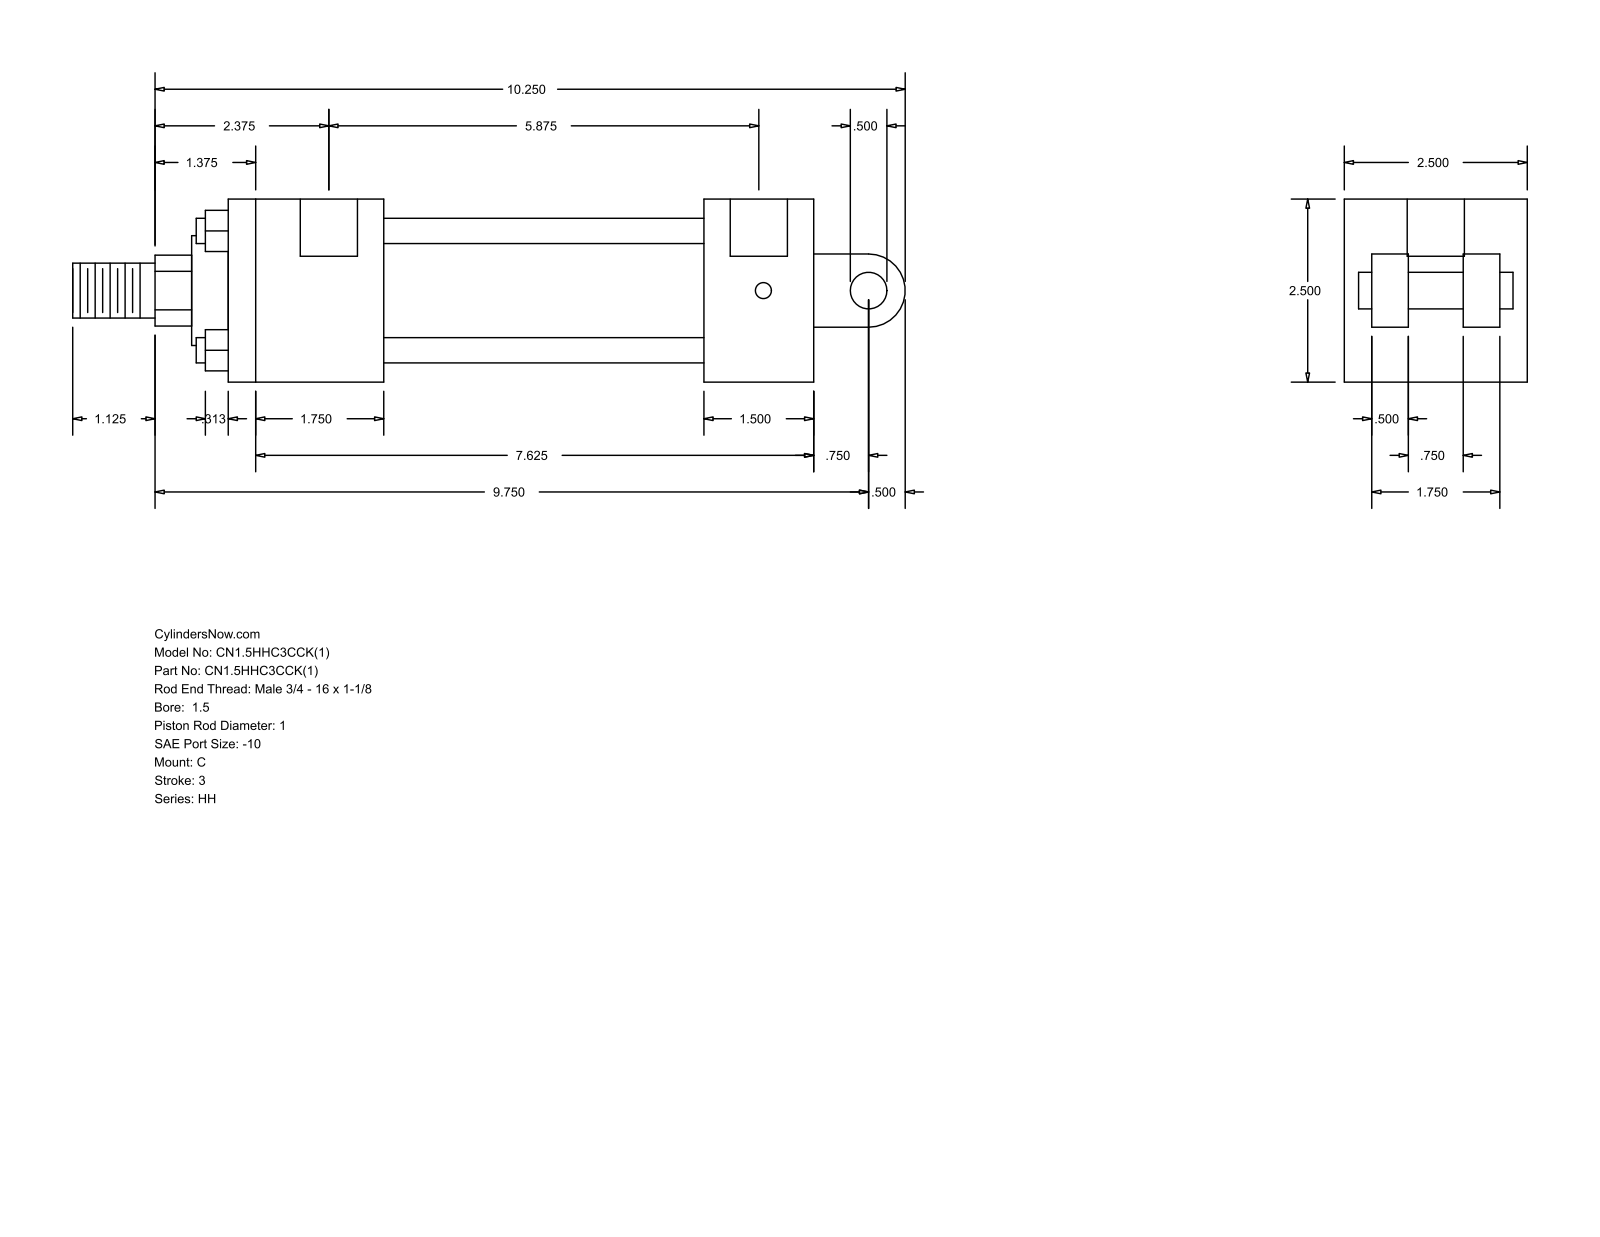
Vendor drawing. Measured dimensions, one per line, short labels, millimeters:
name: HH_C__0150_1
written by: GSSL Pune (CONFIG_CONTROL_DESIGN)
unit: mm
bodies: 0 solids, 99 faces (70 planar, 29 cylindrical, 0 other)
size: 288.93 × 63.5 × 63.5
holes: 4× ⌀5.56, 2× ⌀19.84
bosses: 4× ⌀8.76, 1× ⌀44.45, 1× ⌀38.1, 1× ⌀25.4, 1× ⌀19.05, 1× ⌀12.7
rounds: 1× R12.29, 1× R12.7
face distances: 63.5, 53.98, 38.1, 111.12, 149.22, 165.1, 203.2, 12.7, 22.22, 41.28
hole spacings: 1.59, 150.81, 152.4, 149.22
